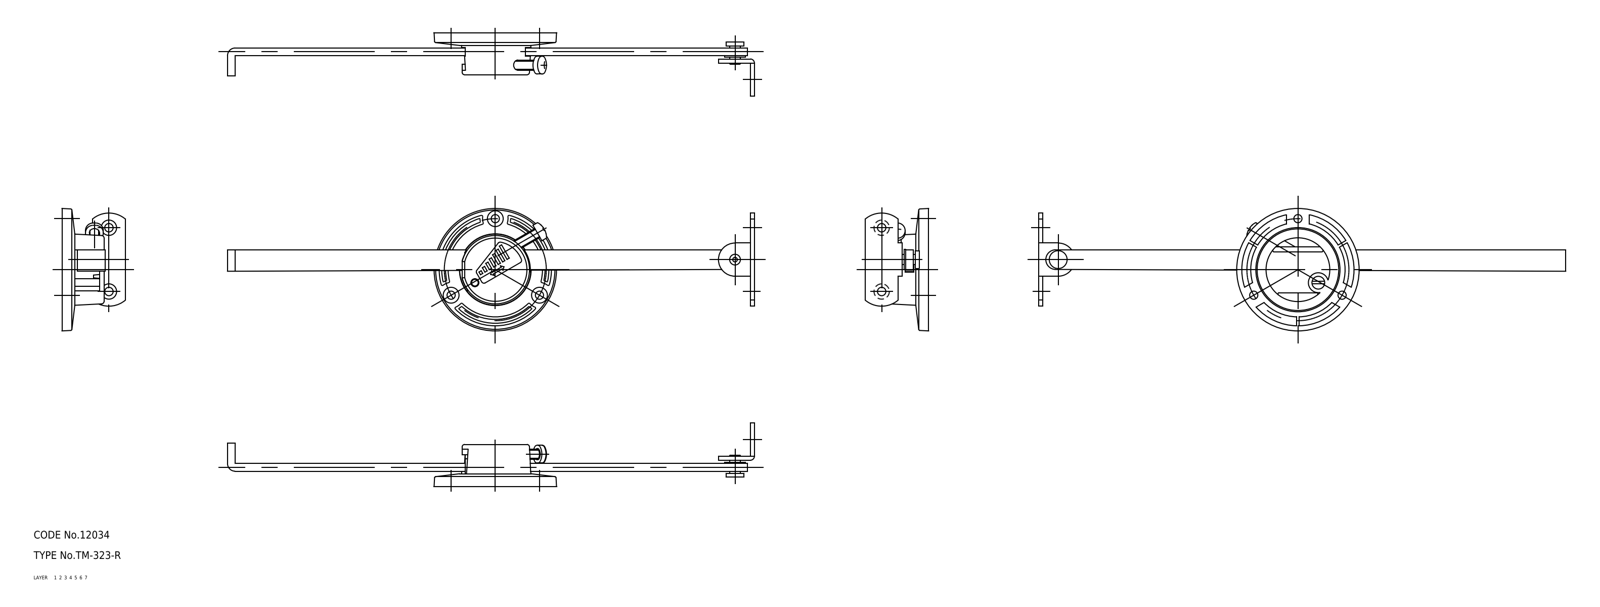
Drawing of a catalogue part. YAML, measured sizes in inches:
part_name: "67121234; 67121247; 67121260"
step_written_by: "CADfix (AUTOMOTIVE_DESIGN)"
units: inches
bodies: {solids: 3, faces: 243, planar: 0, cylindrical: 0, other: 243}
overall_size: [8.134, 1.89, 0.98]
volume: 1.006
surface_area: 23.04
